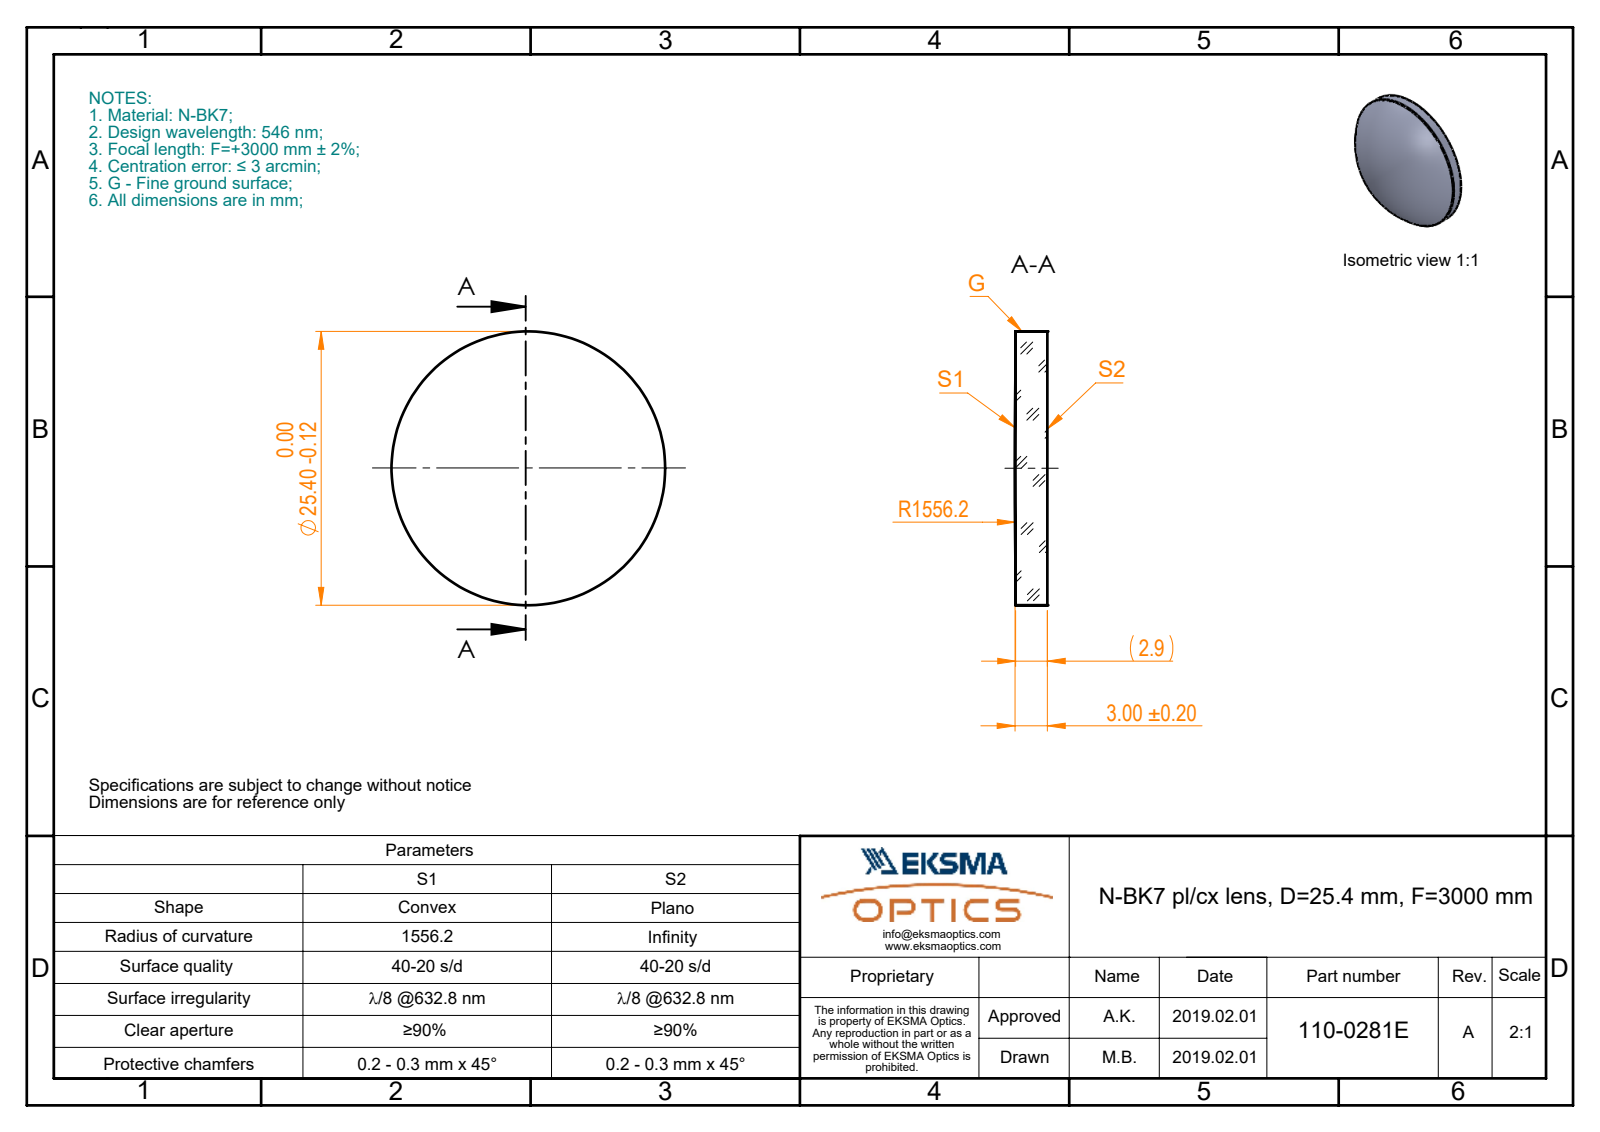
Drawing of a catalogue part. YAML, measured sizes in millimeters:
part_name: "110-0281E BK7 pl-cx 25.4 F3000"
step_written_by: "SolidWorks 2017 (CONFIG_CONTROL_DESIGN)"
units: millimeters
bodies: {solids: 1, faces: 5, planar: 1, cylindrical: 2, other: 2}
overall_size: [25.4, 25.4, 3]
volume: 1507
surface_area: 1249
round_bosses_or_shafts:
  - {diameter: 25.4, count: 1}
